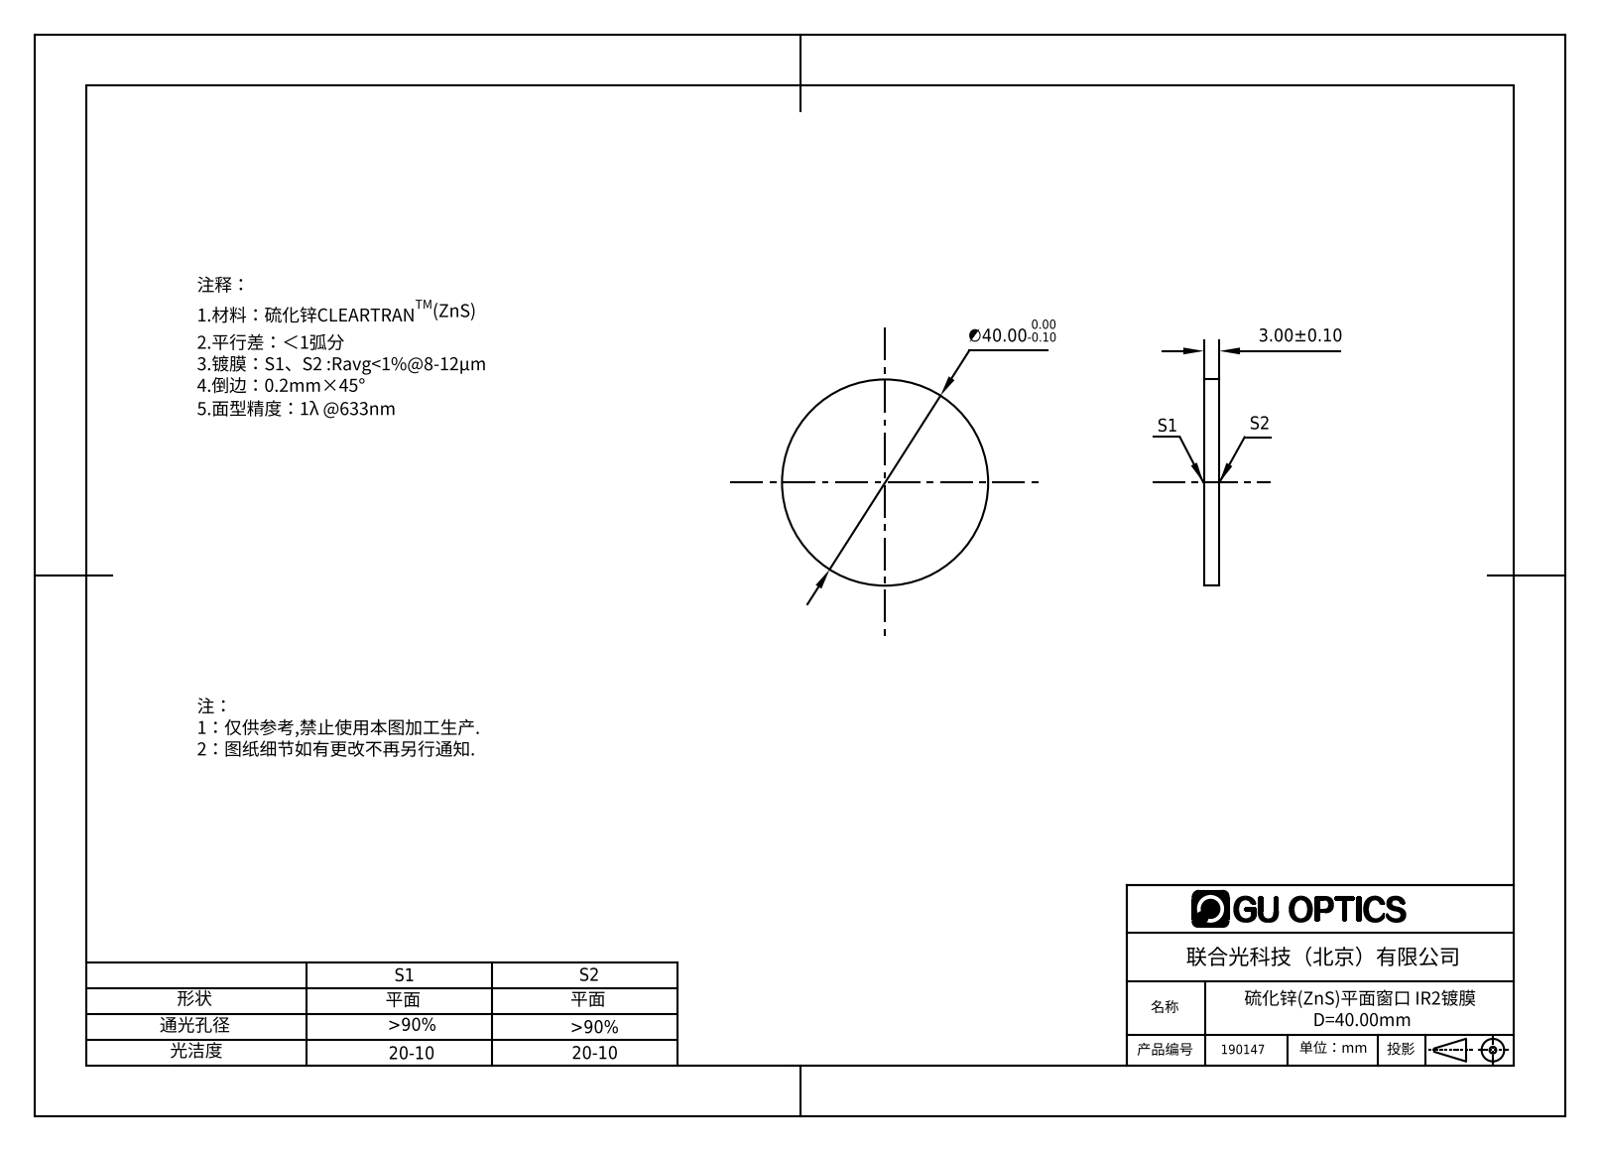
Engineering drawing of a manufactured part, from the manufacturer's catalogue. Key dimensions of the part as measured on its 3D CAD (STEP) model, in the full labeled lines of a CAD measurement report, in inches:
Part name (STEP PRODUCT): 190146
STEP written by: SolidWorks 2016 (AUTOMOTIVE_DESIGN)
Units: inches
Bodies: 1 solid, 4 faces (2 planar, 2 cylindrical, 0 other)
Overall size (bounding box): 1.575 × 1.575 × 0.118
Volume: 0.23 in³ · Surface area: 4.48 in²
Round bosses / shafts (diameter × count): ⌀1.575 ×1
Main face-to-face distances: 0.118
